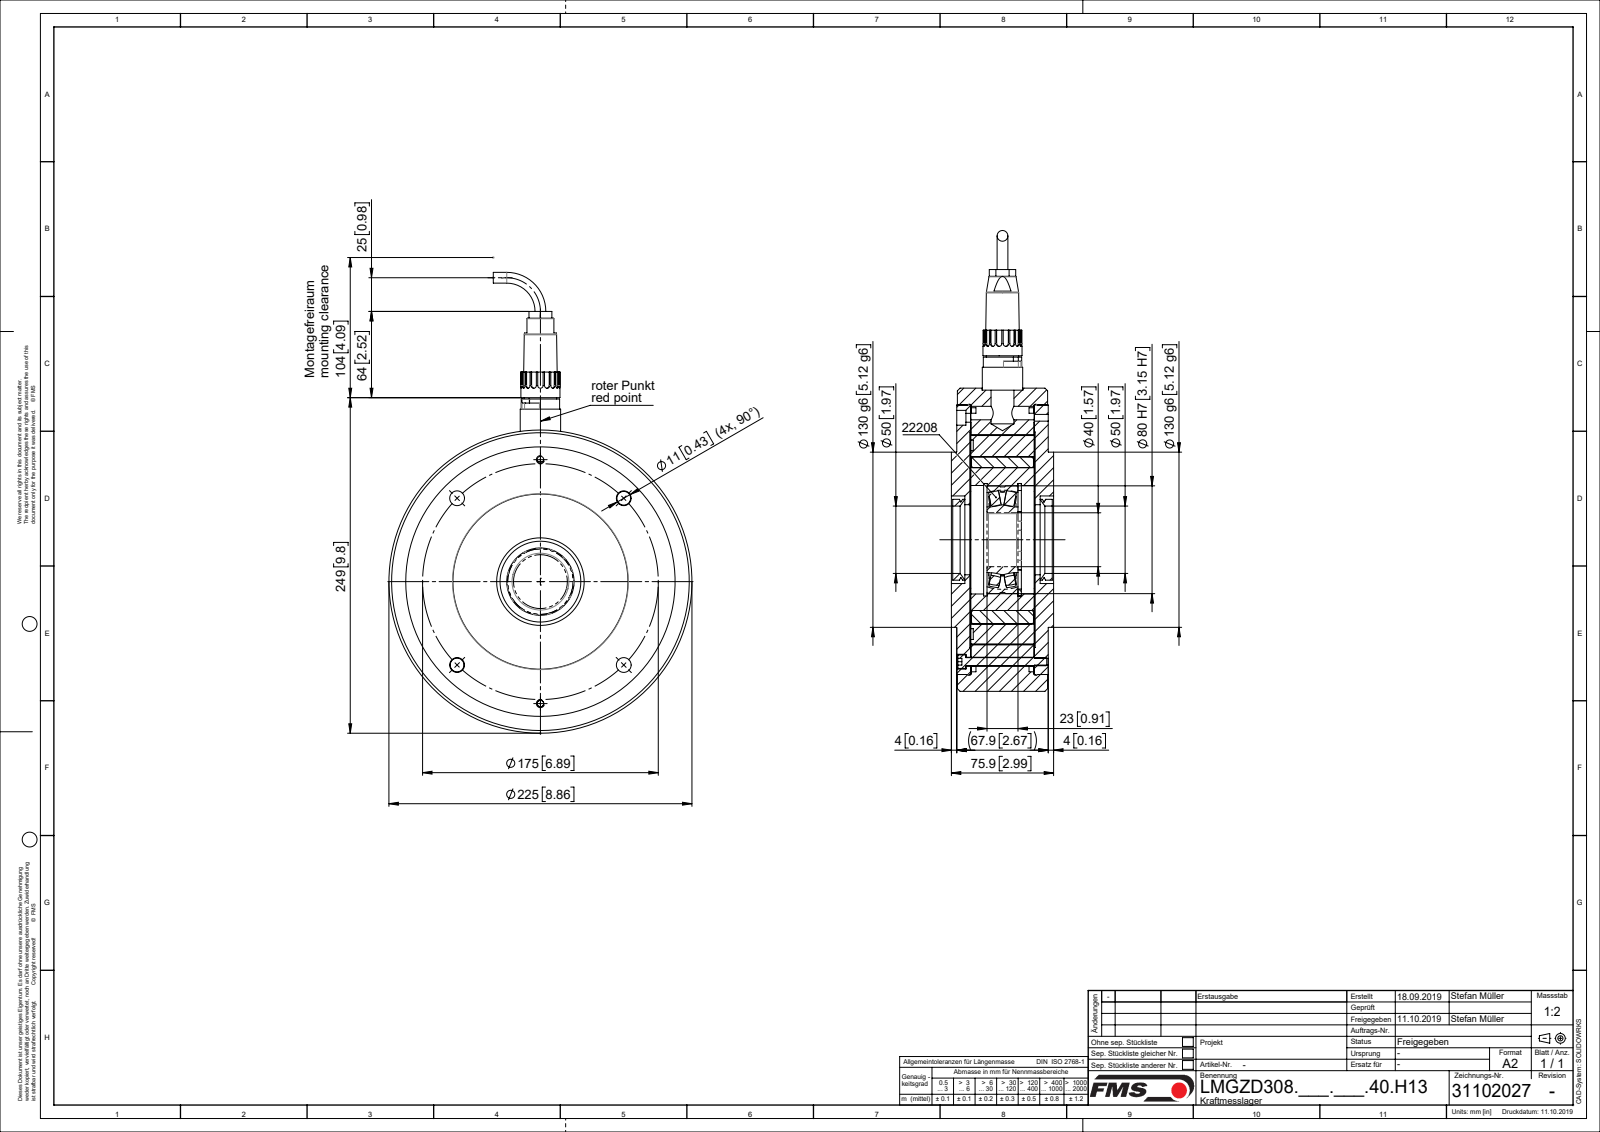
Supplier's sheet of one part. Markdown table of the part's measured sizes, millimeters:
| quantity | value |
| --- | --- |
| part name | 49027_01; 31102026_01; 49651-05_stp_01; Kabeldose_Kunstst_7pol_01 (+8 more) |
| STEP written by | SolidWorks 2018 (CONFIG_CONTROL_DESIGN) |
| units | millimeters |
| bodies | 51 solids, 859 faces (228 planar, 350 cylindrical, 281 other) |
| overall size | 342 × 225 × 75.9 |
| volume | 2 449 000 mm³ |
| surface area | 454 802 mm² |
| round holes (diameter × count) | 11 × 6, 2.5 × 4, 3.2 × 3, 3 × 2, 3.4 × 2, 3.6 × 2, 5 × 2, 6.6 × 2, 10 × 2, 10.2 × 2, 8 × 1, 10.5 × 1 |
| round bosses / shafts (diameter × count) | 2.15 × 7, 5.5 × 2, 3 × 2, 225 × 1, 199 × 1, 188 × 1, 132 × 1, 130 × 1 |
| partial cylindrical surfaces (radius × count) | 2 × 17, 0.1 × 4, 11 × 4, 3 × 2, 4.91 × 2, 33.25 × 1, 79 × 1, 82 × 1 |
| main face-to-face distances | 47.25, 10.2, 48, 0.75, 0.5, 47.75, 9.7, 10.45, 57.45, 57.7 |
| hole center spacings | 16.26, 22.47, 23, 62.02, 68.17, 87.5, 123.74, 134.45 |
